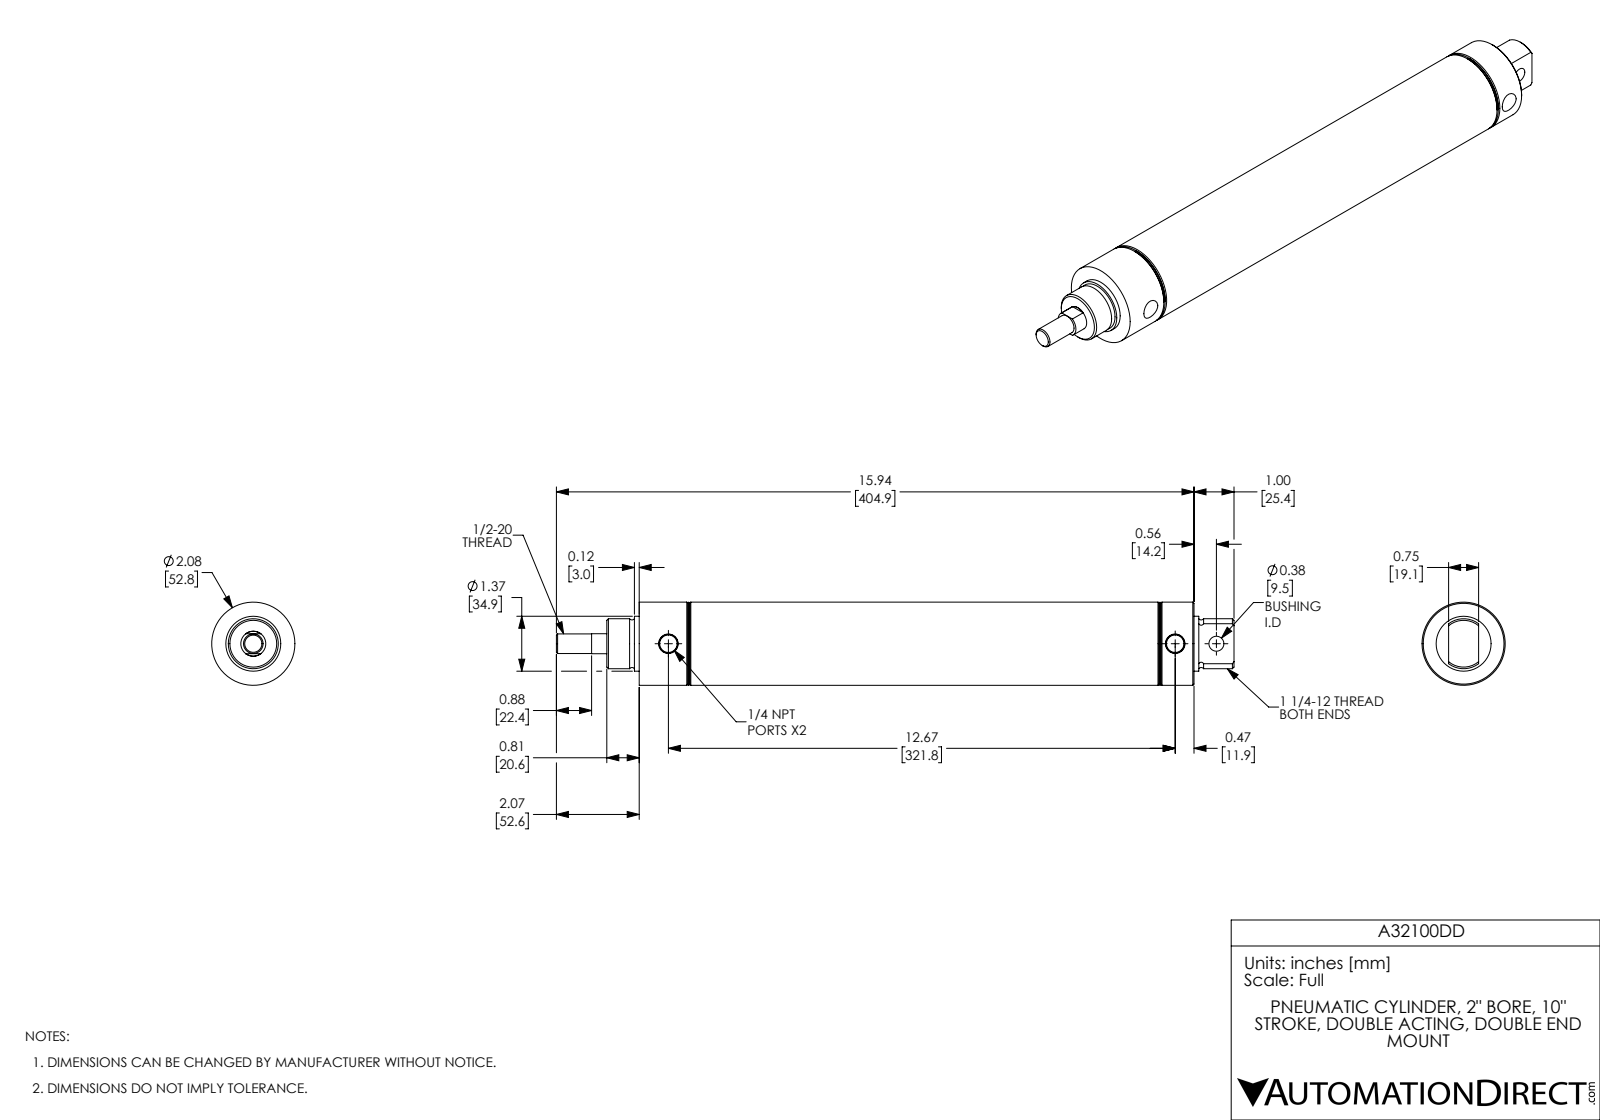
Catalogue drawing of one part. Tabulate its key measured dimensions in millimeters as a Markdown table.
| quantity | value |
| --- | --- |
| part name | A32100DD; A32100DD-Rod; A32100DD-MainBody |
| STEP written by | SolidWorks 2017 (AUTOMOTIVE_DESIGN) |
| units | millimeters |
| bodies | 2 solids, 88 faces (20 planar, 30 cylindrical, 38 other) |
| overall size | 430.3 × 52.8 × 52.8 |
| volume | 337 700 mm³ |
| surface area | 142 000 mm² |
| round holes (diameter × count) | 11.1 × 2, 9.5 × 1, 15.9 × 1, 50.8 × 1 |
| round bosses / shafts (diameter × count) | 52.8 × 1, 34.9 × 1, 31.8 × 1, 12.5 × 1 |
| main face-to-face distances | 12.7, 266.7, 254, 309.5, 296.8, 42.8, 42.8, 55.5, 309.5, 352.3 |
| hole center spacings | 26.2, 321.8, 348 |
